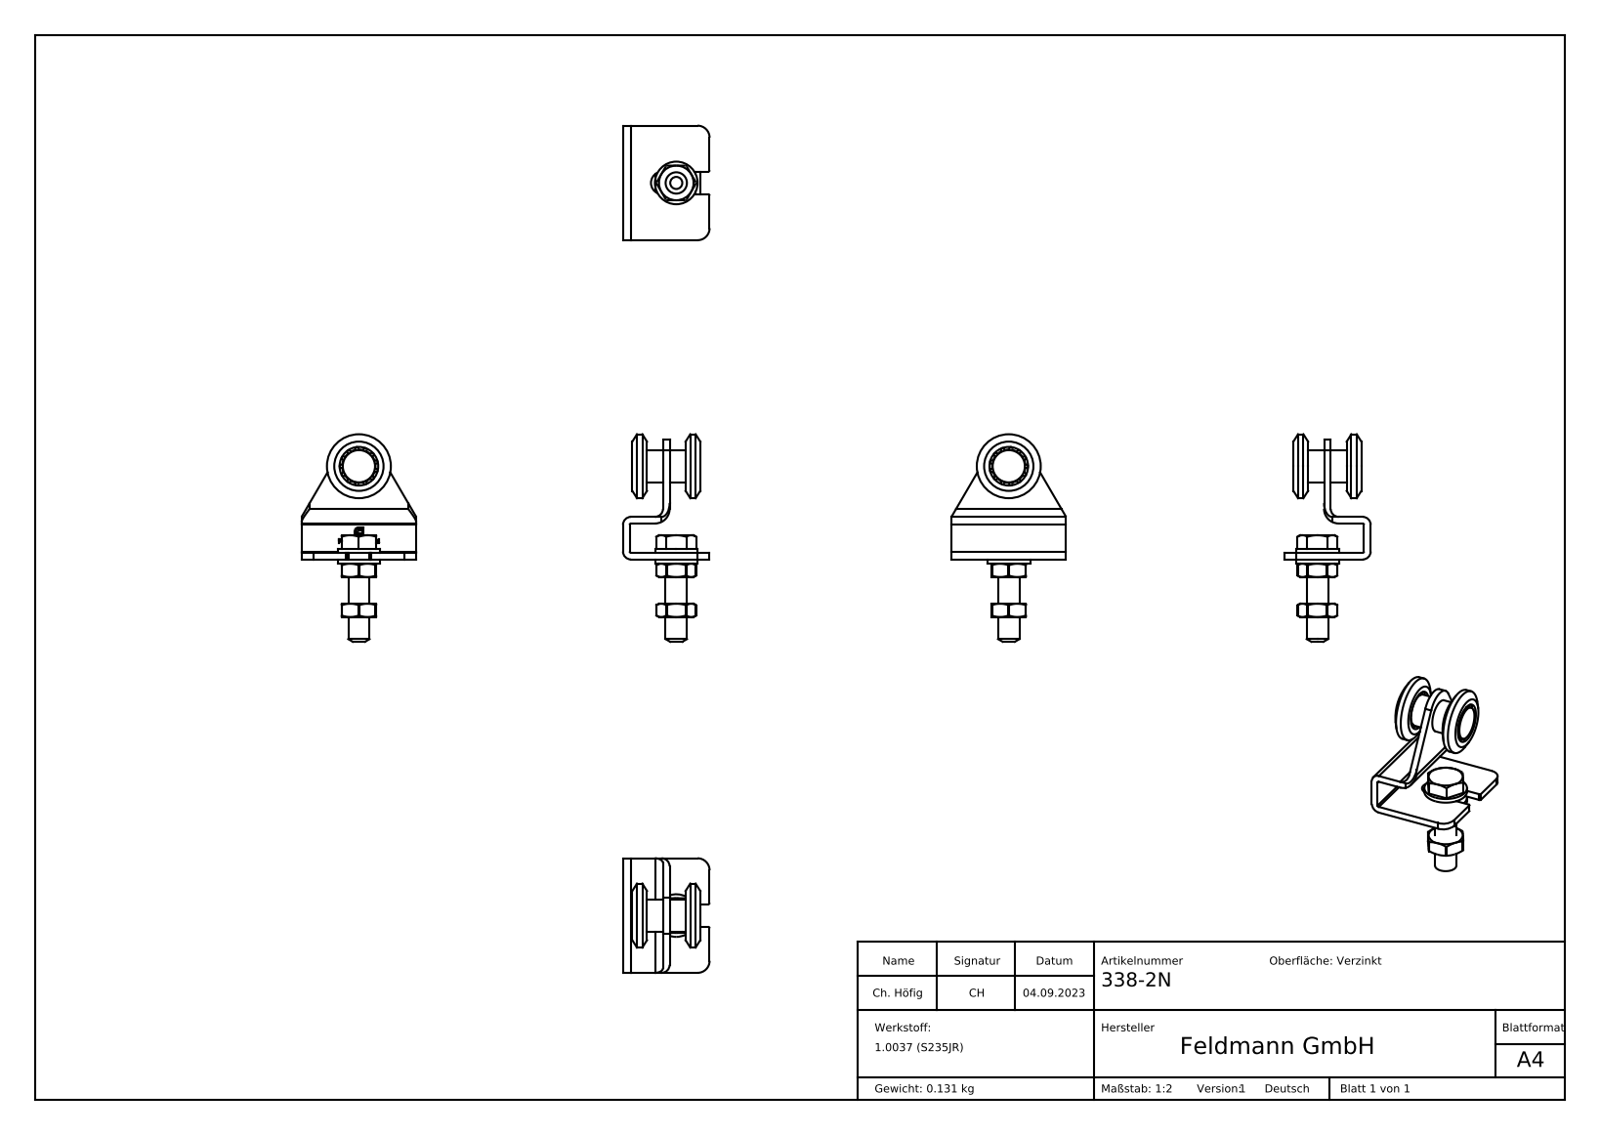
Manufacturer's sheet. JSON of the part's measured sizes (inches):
{"part_name": "338-2N Teil1_338-2N Teil1; 338-2N; DIN 125 M4-M20_DIN 125 M8; DIN 931_DIN 931 M8x35 (+1 more)", "step_written_by": "SolidWorks 2018 (CONFIG_CONTROL_DESIGN)", "units": "inches", "bodies": {"solids": 60, "faces": 438, "planar": 181, "cylindrical": 47, "other": 210}, "overall_size": [3.067, 1.693, 1.28], "volume_in3": 1.024, "surface_area_in2": 20.68, "round_holes": [[0.268, 1], [0.331, 1], [0.571, 1]], "round_bosses_or_shafts": [[0.945, 1], [0.63, 1], [0.492, 1], [0.476, 1], [0.453, 1], [0.315, 1]], "partial_cylinders_radius": [[0.02, 10], [0.118, 5], [0.177, 2], [0.167, 1], [0.217, 1], [0.315, 1]], "face_to_face_distances": [0.098, 0.591, 0.531, 0.689, 0.063, 0.161, 0.453, 0.551, 0.492, 0.433]}
